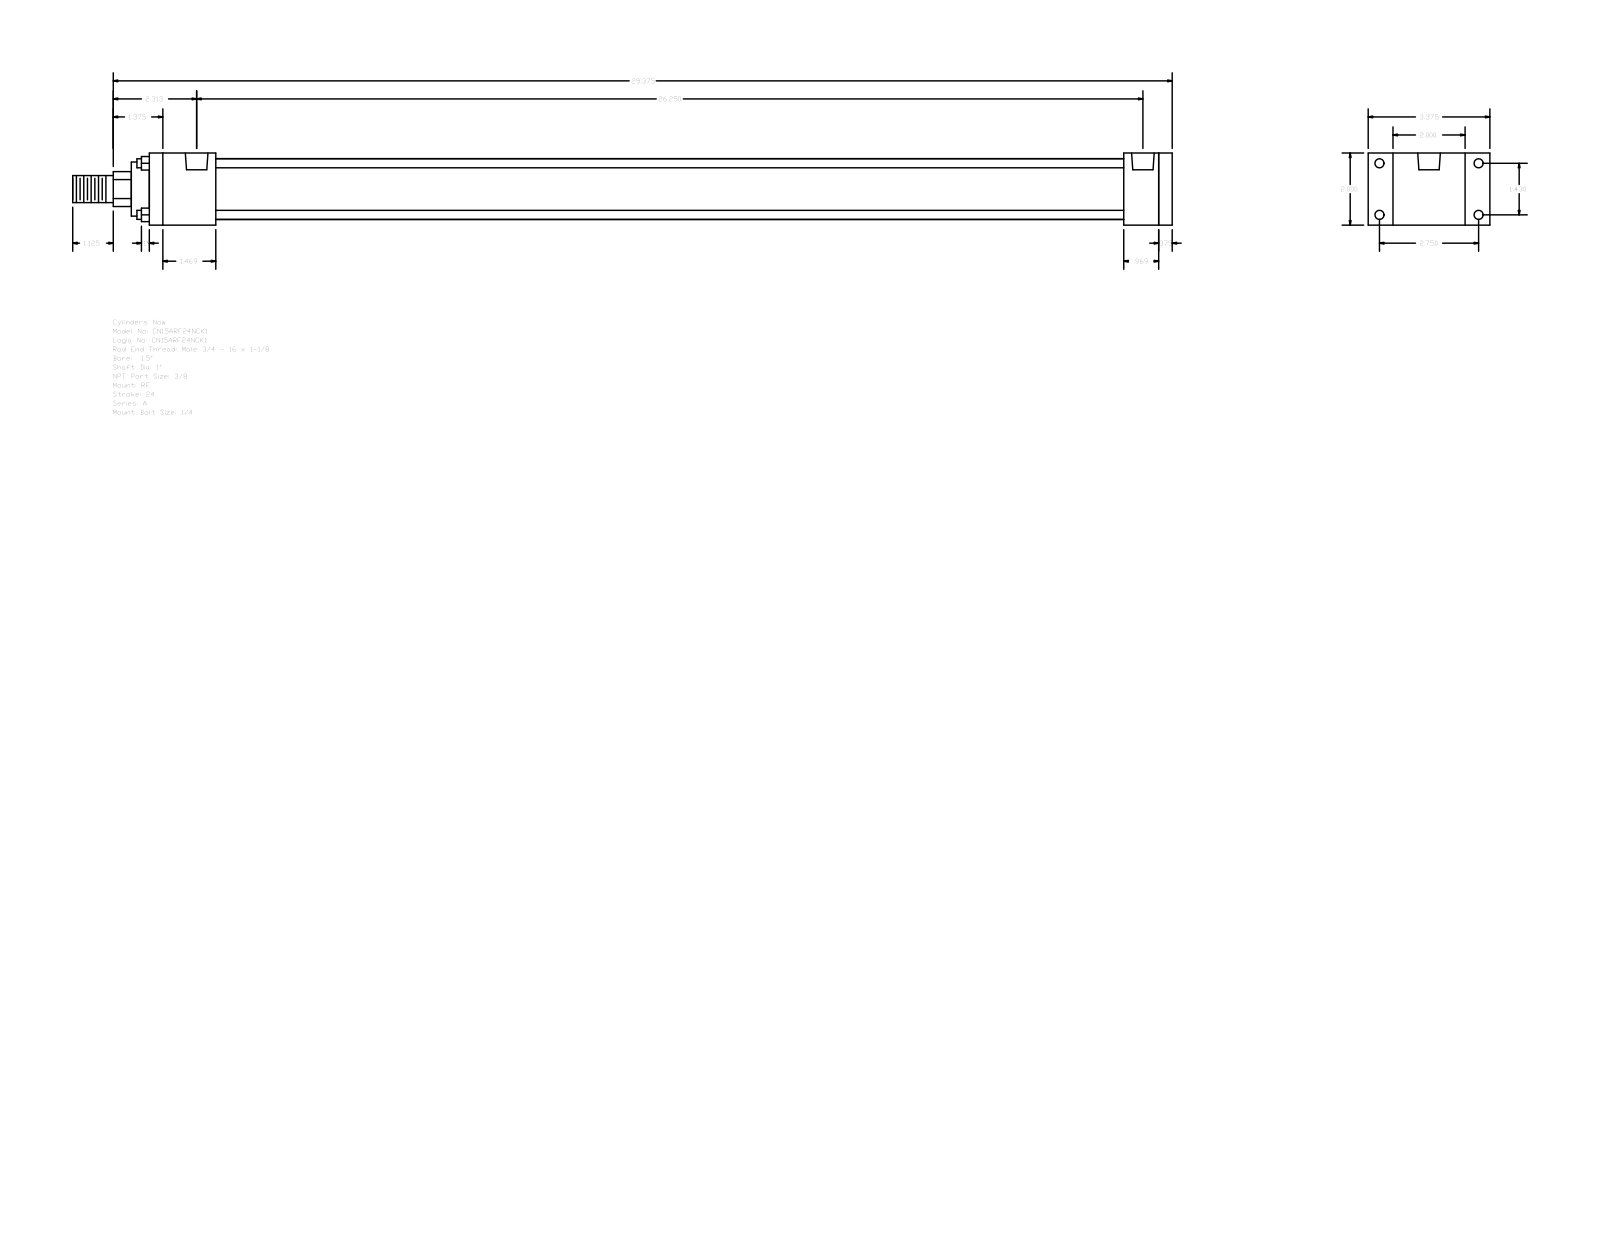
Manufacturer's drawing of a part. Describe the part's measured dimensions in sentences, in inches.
The part is named "A_RF__0150_1". Its 3-D file was written by "GSSL Pune (CONFIG_CONTROL_DESIGN)". It is 0 solids with 92 faces: 64 planar, 28 cylindrical and 0 other. Overall it measures 30.5 by 3.375 by 2 inches. Round holes: 4 of diameter 0.219, 4 of diameter 0.25, 2 of diameter 0.627. Round bosses or shafts: 4 of diameter 0.25, 1 of diameter 1.69, 1 of diameter 1.5, 1 of diameter 1, 1 of diameter 0.75. Partial cylindrical surfaces (rounded edges, fillets, slot ends): 1 of radius 0.484. The main face-to-face distances are 2, 0.375, 28, 28.375, 27.031, 0.969, 1.344, 1.844, 25.187, 26.156. The hole center spacings are 0.156, 1.43, 2.75, 3.099, 25.937, 26.094, 26.25.
